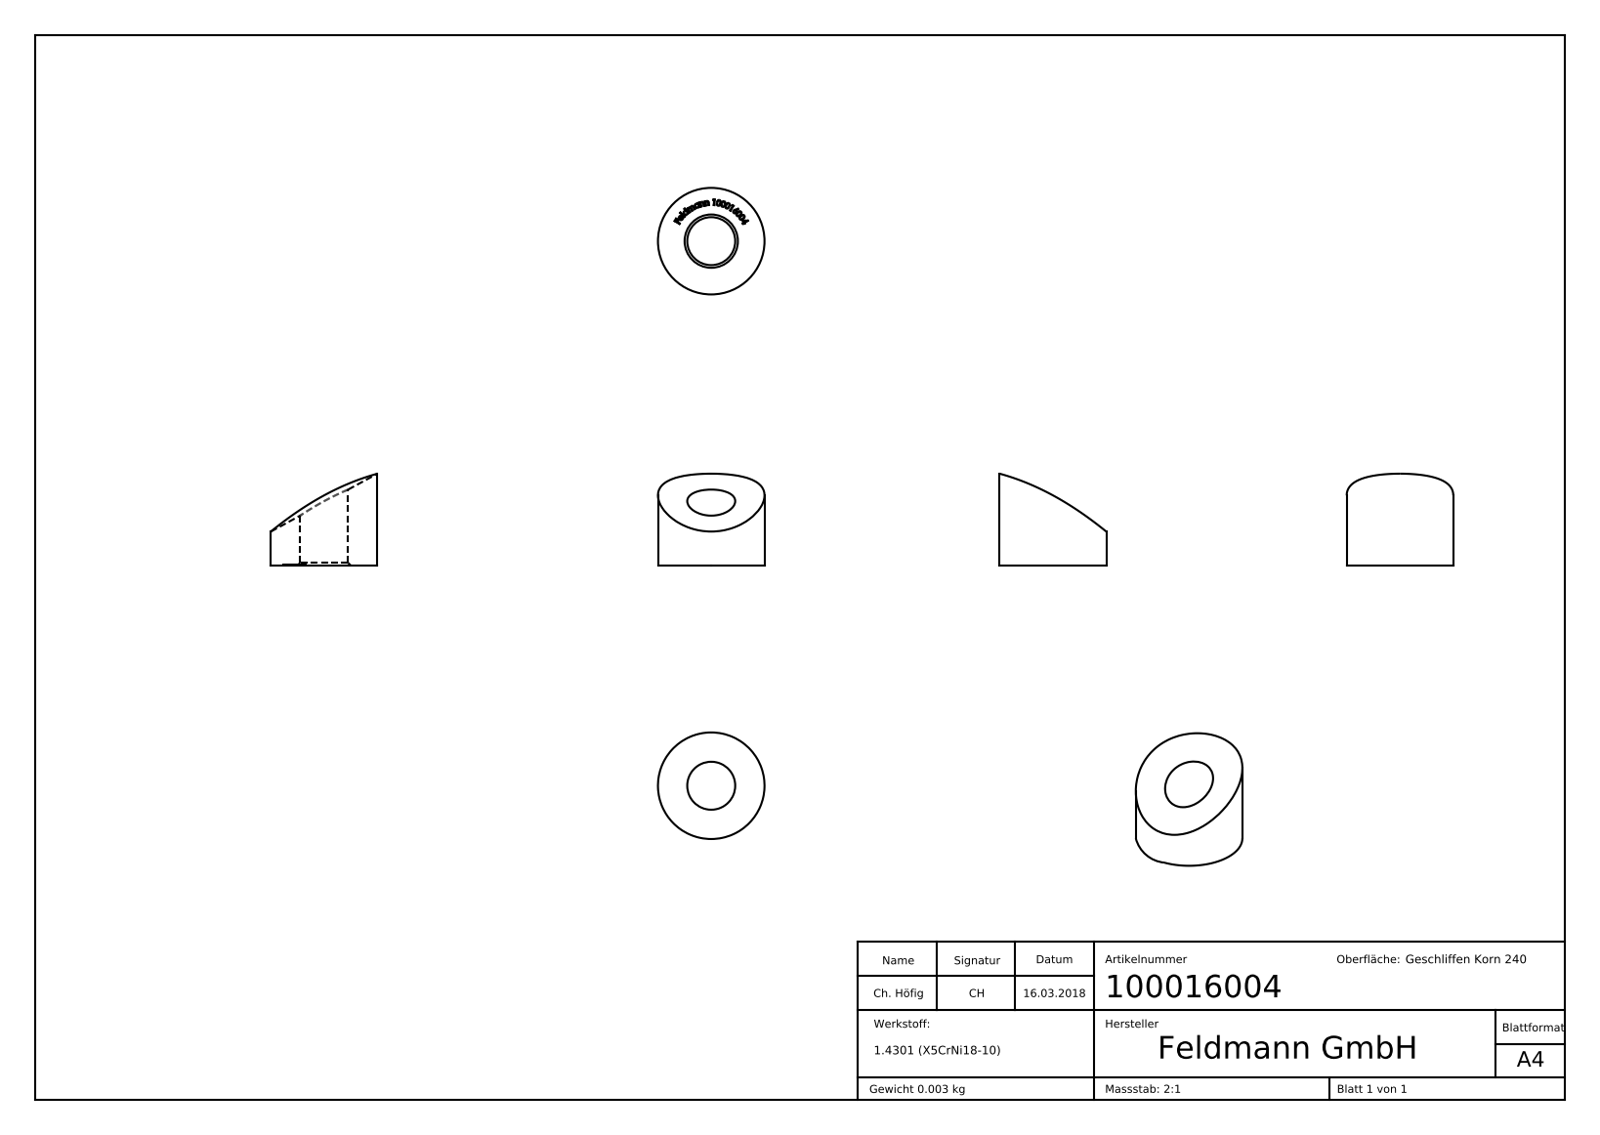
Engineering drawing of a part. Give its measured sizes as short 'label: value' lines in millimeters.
name: 100016004
written by: SolidWorks 2015 (CONFIG_CONTROL_DESIGN)
unit: mm
bodies: 1 solid, 219 faces (110 planar, 5 cylindrical, 104 other)
size: 10 × 10 × 8.62
volume: 382 mm³; area: 417 mm²
holes: 1× ⌀4.5
bosses: 1× ⌀10
rounds: 1× R21.2
face distances: 0.34, 0.53, 0.58, 0.39, 0.54, 0.48, 1.26
